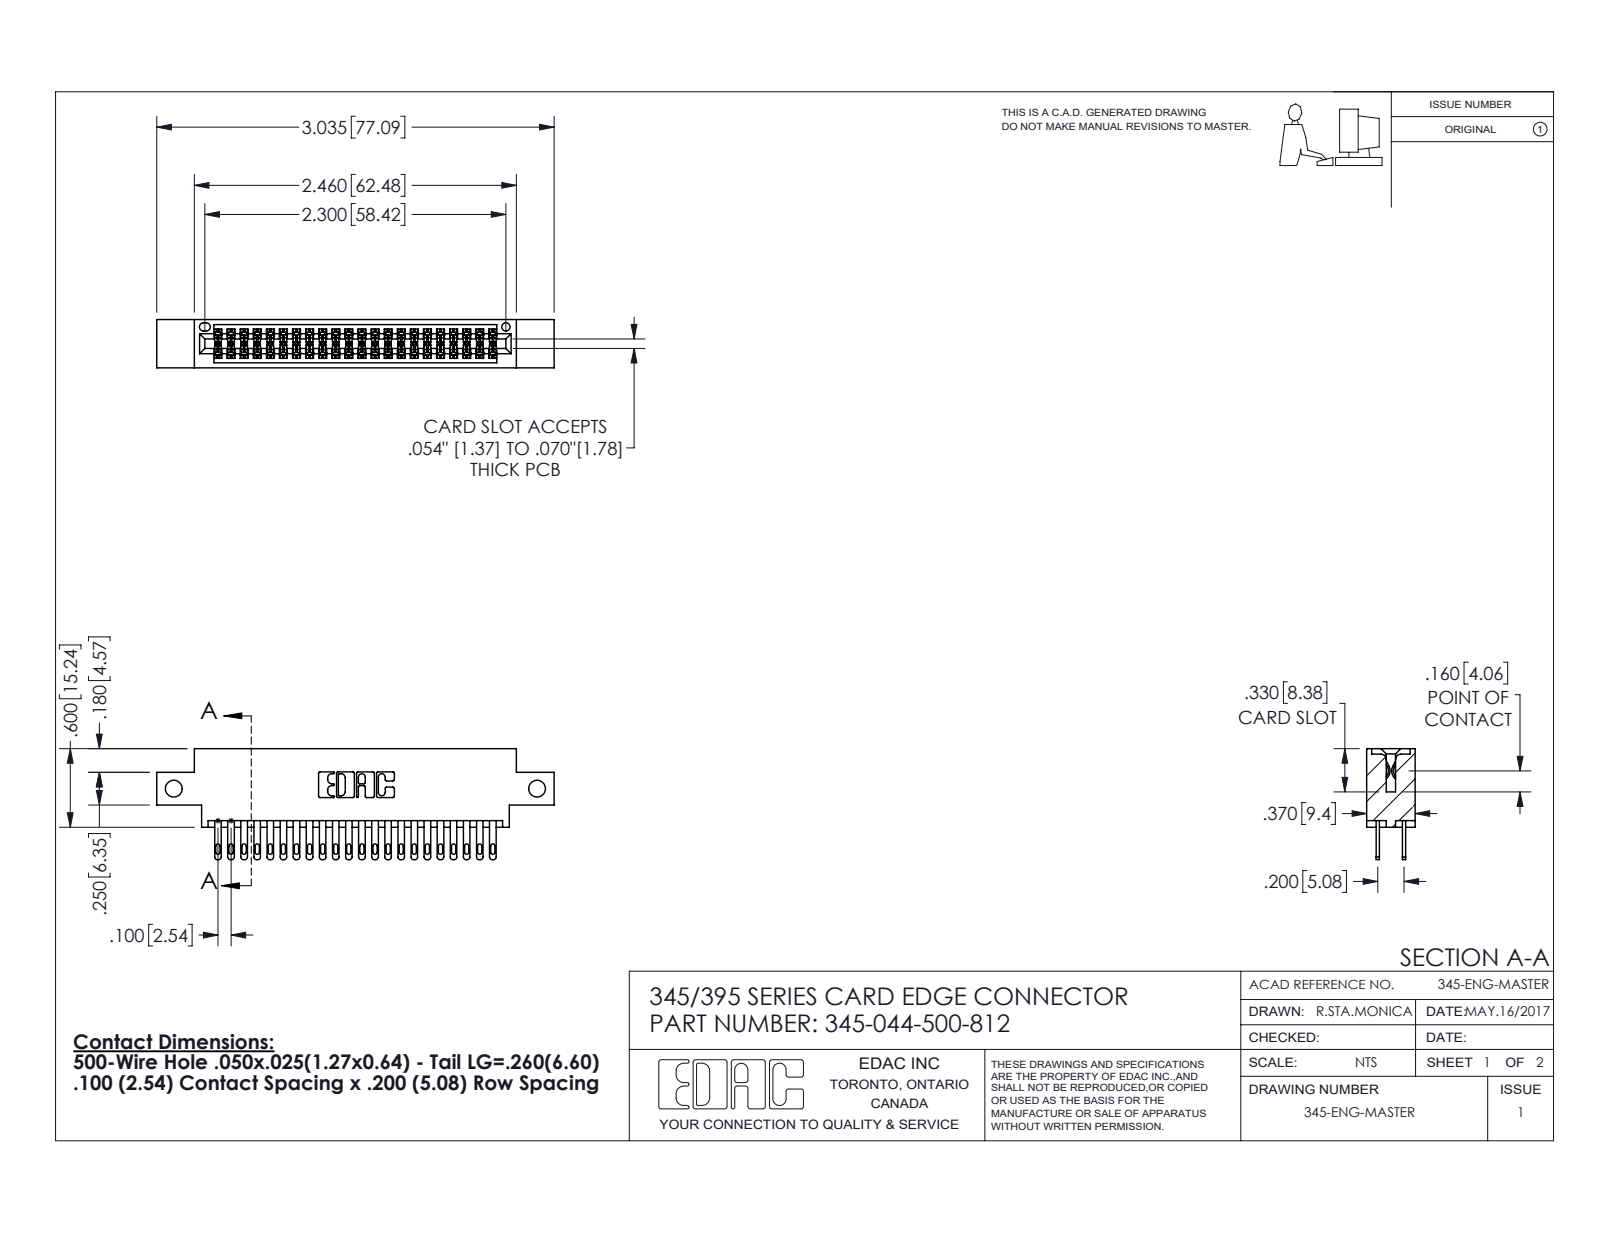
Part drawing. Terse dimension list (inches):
name: 345 Part_0.170 Offset - Side Mount; 345-292-001_345-293-100; 345-044-500-812
written by: SolidWorks 2016 (CONFIG_CONTROL_DESIGN)
unit: in
bodies: 45 solids, 2154 faces (1272 planar, 882 cylindrical, 0 other)
size: 3.035 × 0.847 × 0.37
volume: 0.442 in³; area: 16.69 in²
holes: 2× ⌀0.128, 1× ⌀0.064
rounds: 66× R0.006, 44× R0.016, 44× R0.02, 22× R0.01, 6× R0.007, 6× R0.031, 3× R0.026, 2× R0.014
face distances: 0.072, 0.298, 0.2, 0.098, 0.272, 0.025, 0.37, 0.225, 0.175, 0.15
hole spacings: 2.775
